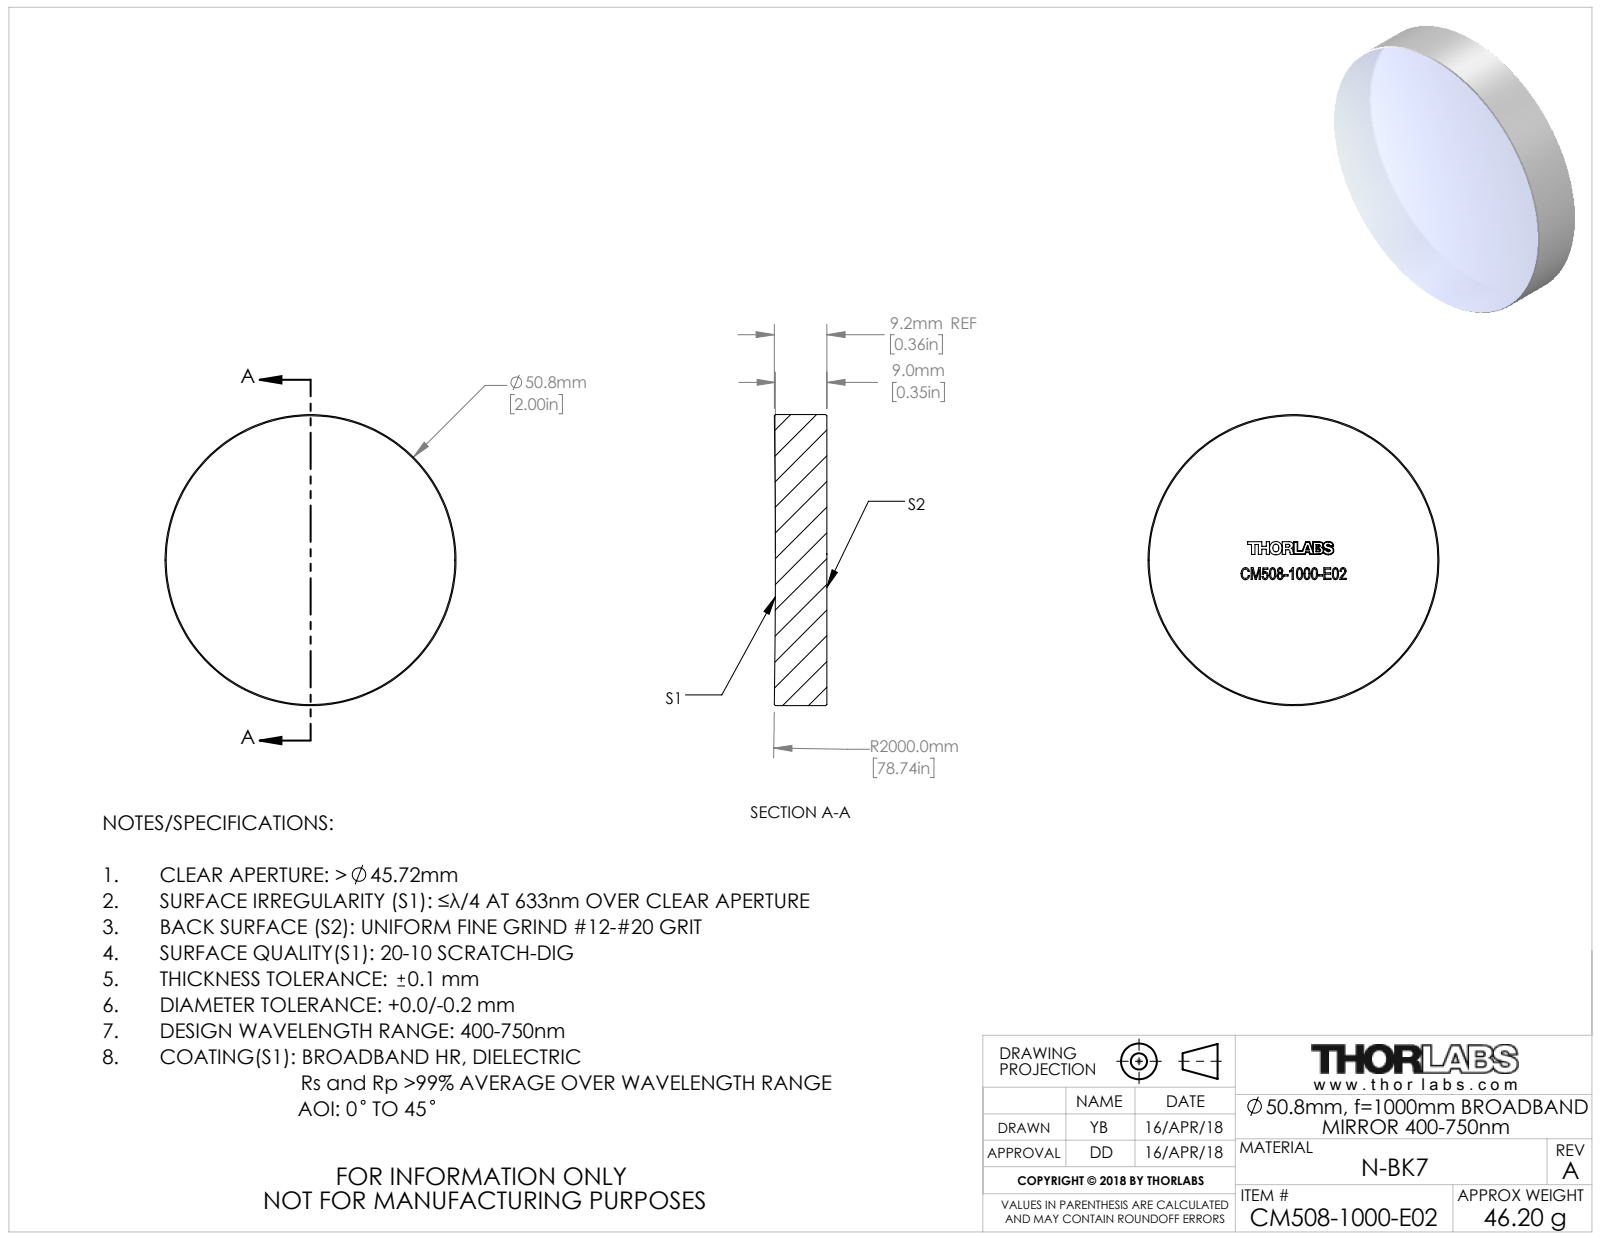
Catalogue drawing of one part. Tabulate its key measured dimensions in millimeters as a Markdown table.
| quantity | value |
| --- | --- |
| part name | TTN153340-E0W |
| STEP written by | SolidWorks 2018 (CONFIG_CONTROL_DESIGN) |
| units | millimeters |
| bodies | 1 solid, 45 faces (37 planar, 2 cylindrical, 6 other) |
| overall size | 50.8 × 50.8 × 9.16 |
| volume | 18 399 mm³ |
| surface area | 5 478 mm² |
| round bosses / shafts (diameter × count) | 50.8 × 1 |
